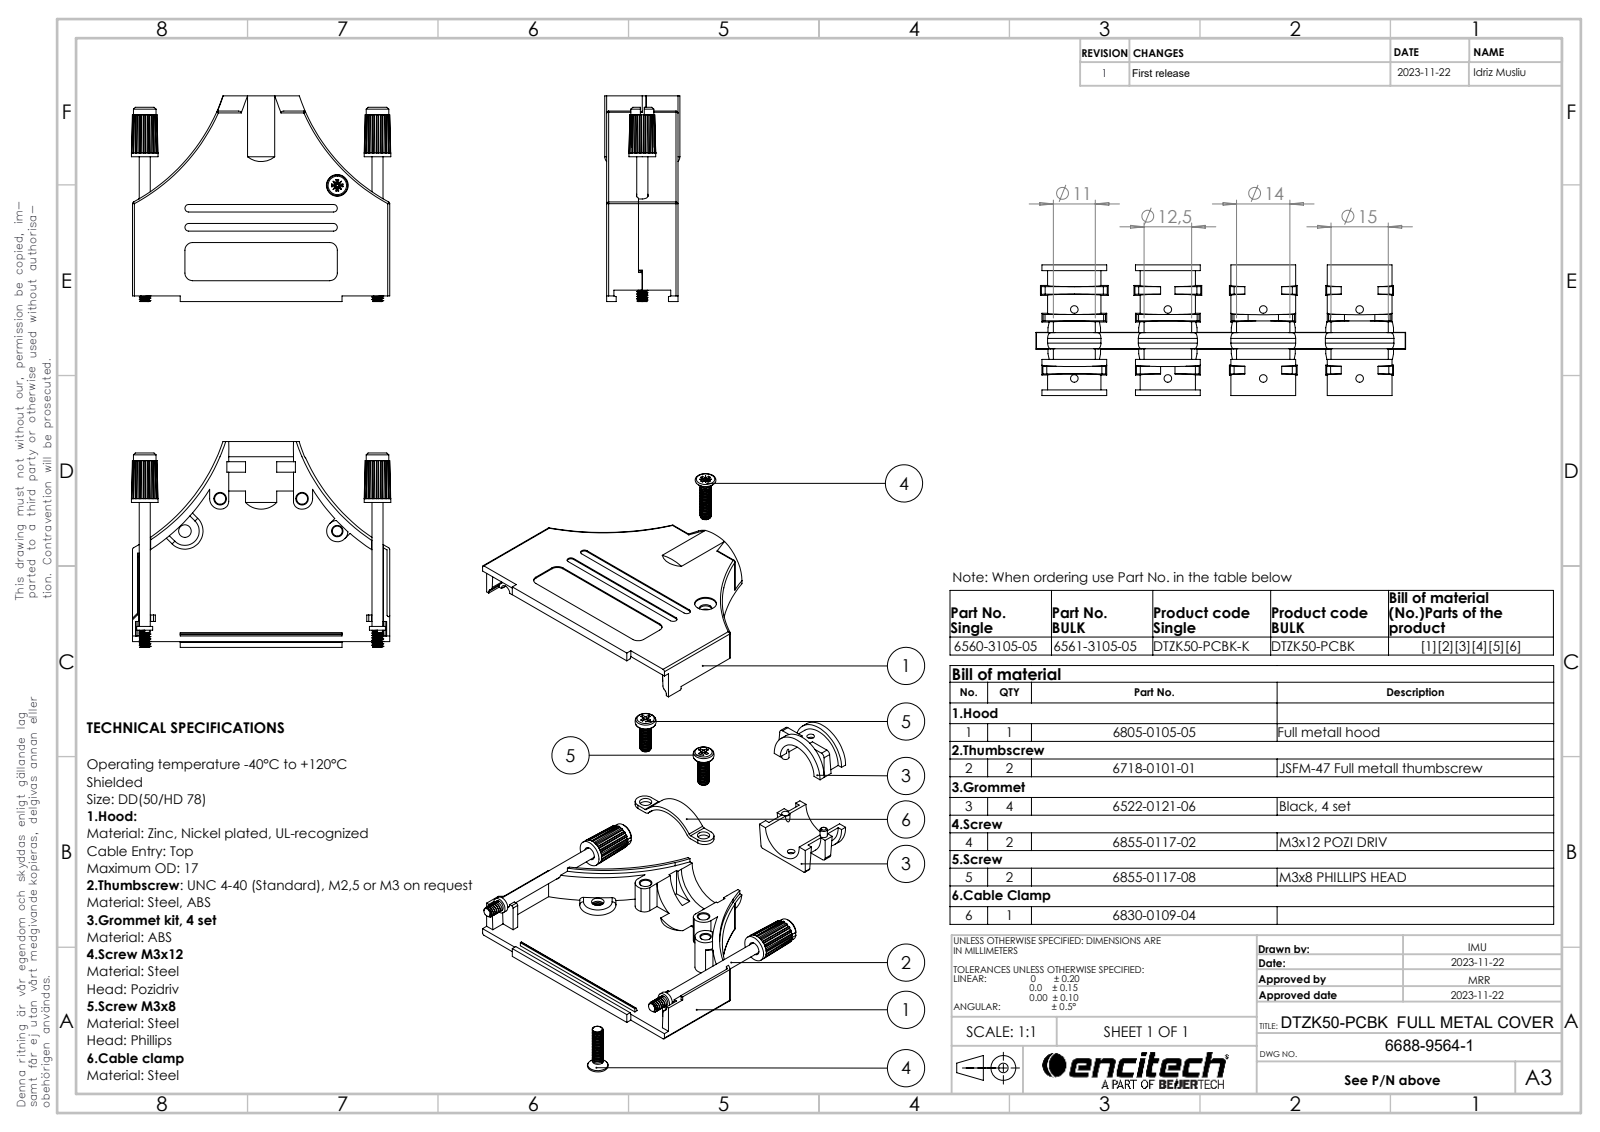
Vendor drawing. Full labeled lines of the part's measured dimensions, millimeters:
Part name (STEP PRODUCT): 6522-0121-06 (12.5 mm LV); 6830-0109-04; 6805-0105-05; 6855-0117-08 (+5 more)
STEP written by: SolidWorks 2021 (AUTOMOTIVE_DESIGN)
Units: millimetres
Bodies: 11 solids, 1015 faces (471 planar, 362 cylindrical, 182 other)
Overall size (bounding box): 68.1 × 54 × 19.7
Volume: 18 194 mm³ · Surface area: 21 542 mm²
Round holes (diameter × count): ⌀2 ×4, ⌀2.6 ×2, ⌀2.9 ×2, ⌀3.1 ×2, ⌀3.2 ×2, ⌀3.3 ×2, ⌀3.31 ×2, ⌀5.7 ×2, ⌀12.5 ×1
Round bosses / shafts (diameter × count): ⌀2.9 ×4, ⌀7 ×2, ⌀6 ×2, ⌀4.2 ×2, ⌀3 ×2, ⌀2.85 ×2, ⌀1.9 ×2, ⌀17 ×1
Partial cylindrical surfaces — rounded edges, fillets, slot ends (radius × count): R0.5 ×22, R1 ×22, R0.1 ×8, R2 ×6, R50 ×6, R0.25 ×4, R0.3 ×2, R0.75 ×2
Main face-to-face distances: 1.9, 16.8, 14.9, 18.7, 18.4, 1.6, 16.5, 7.45, 9.35, 9.05
Hole centre spacings: 7.45, 8.66, 9.02, 11.25, 12.56, 15.03, 19.66, 21.14
